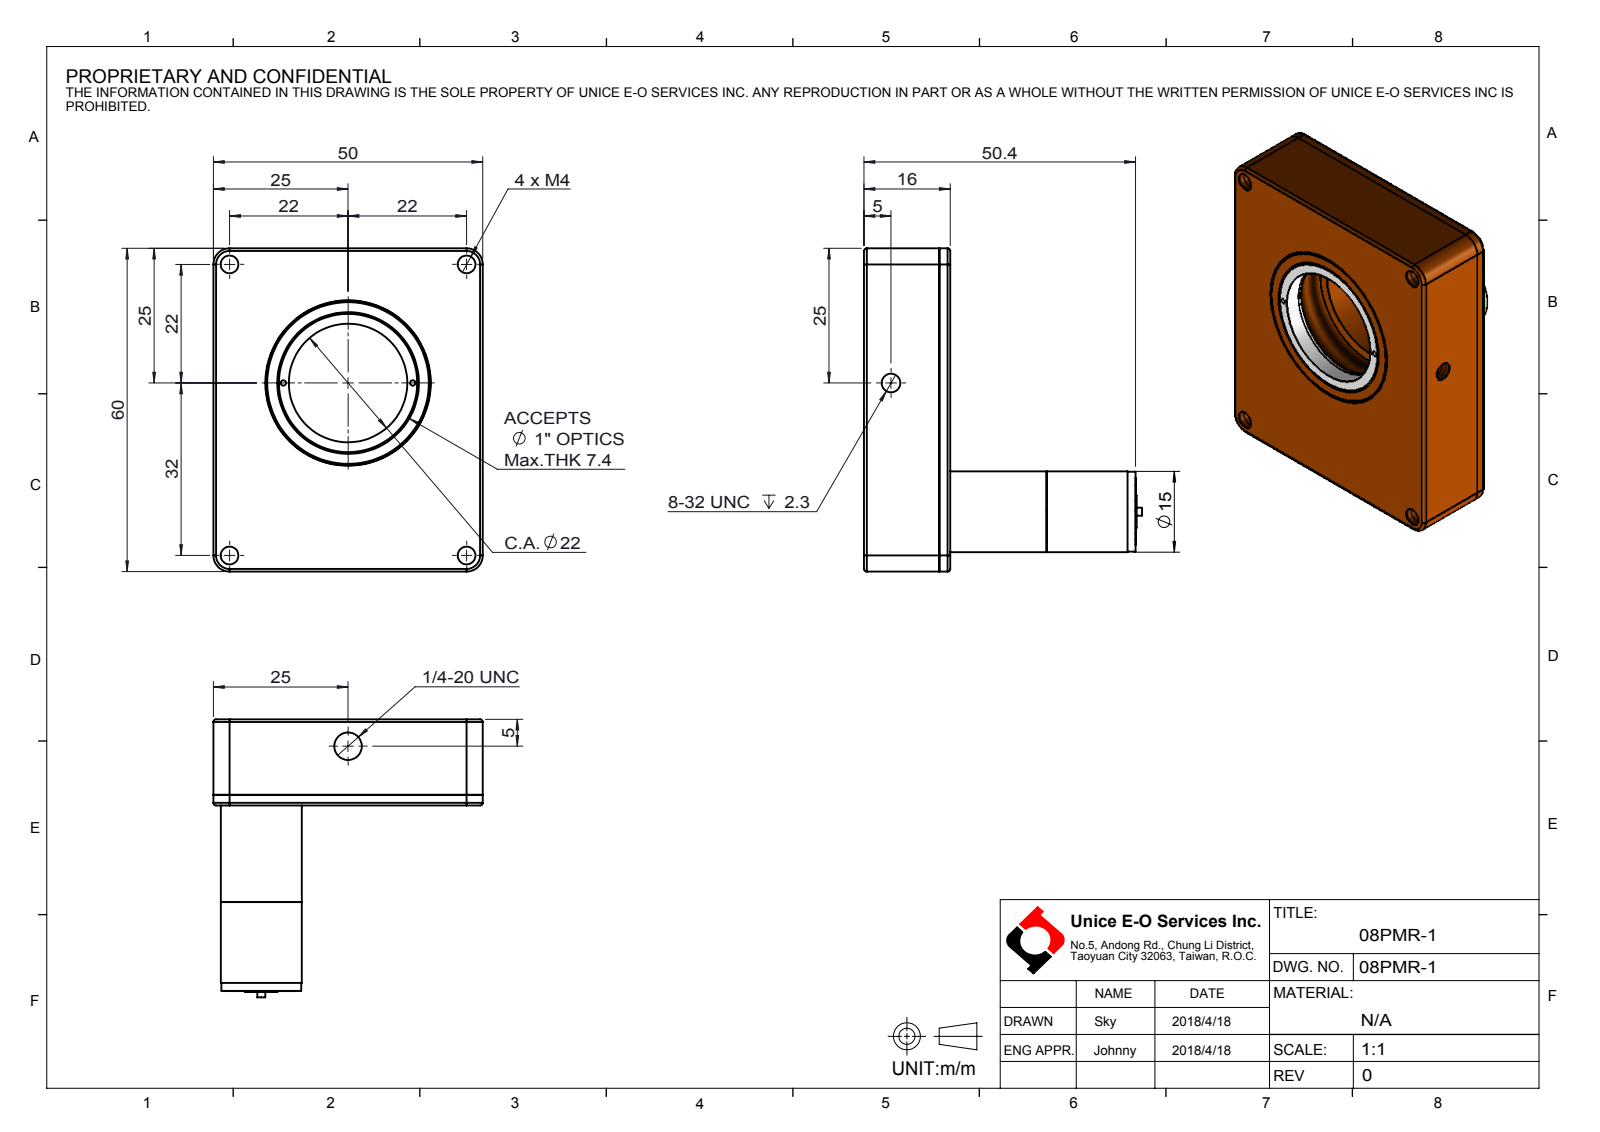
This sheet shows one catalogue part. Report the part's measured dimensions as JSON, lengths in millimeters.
{"part_name": "08PMR-1", "step_written_by": "SolidWorks 2016 (AUTOMOTIVE_DESIGN)", "units": "millimeters", "bodies": {"solids": 0, "faces": 203, "planar": 74, "cylindrical": 97, "other": 32}, "overall_size": [60, 51.6, 50], "round_holes": [[3.3, 4], [1, 2], [1.7, 1], [2.5, 1], [3.45, 1], [5.11, 1], [22, 1], [23, 1], [25.65, 1], [26, 1], [27, 1], [30, 1]], "round_bosses_or_shafts": [[1.8, 7], [5.8, 3], [32, 1], [15, 1], [14.8, 1], [6, 1], [1.6, 1], [1.5, 1]], "partial_cylinders_radius": [[0.5, 8], [3, 4], [7.5, 2]], "face_to_face_distances": [16, 50, 60, 17.9, 33.9, 22.9, 5, 11, 30.3, 12.4], "hole_center_spacings": [12, 24.17, 31.11, 33.53, 38.83, 40.5, 44, 46.69]}
